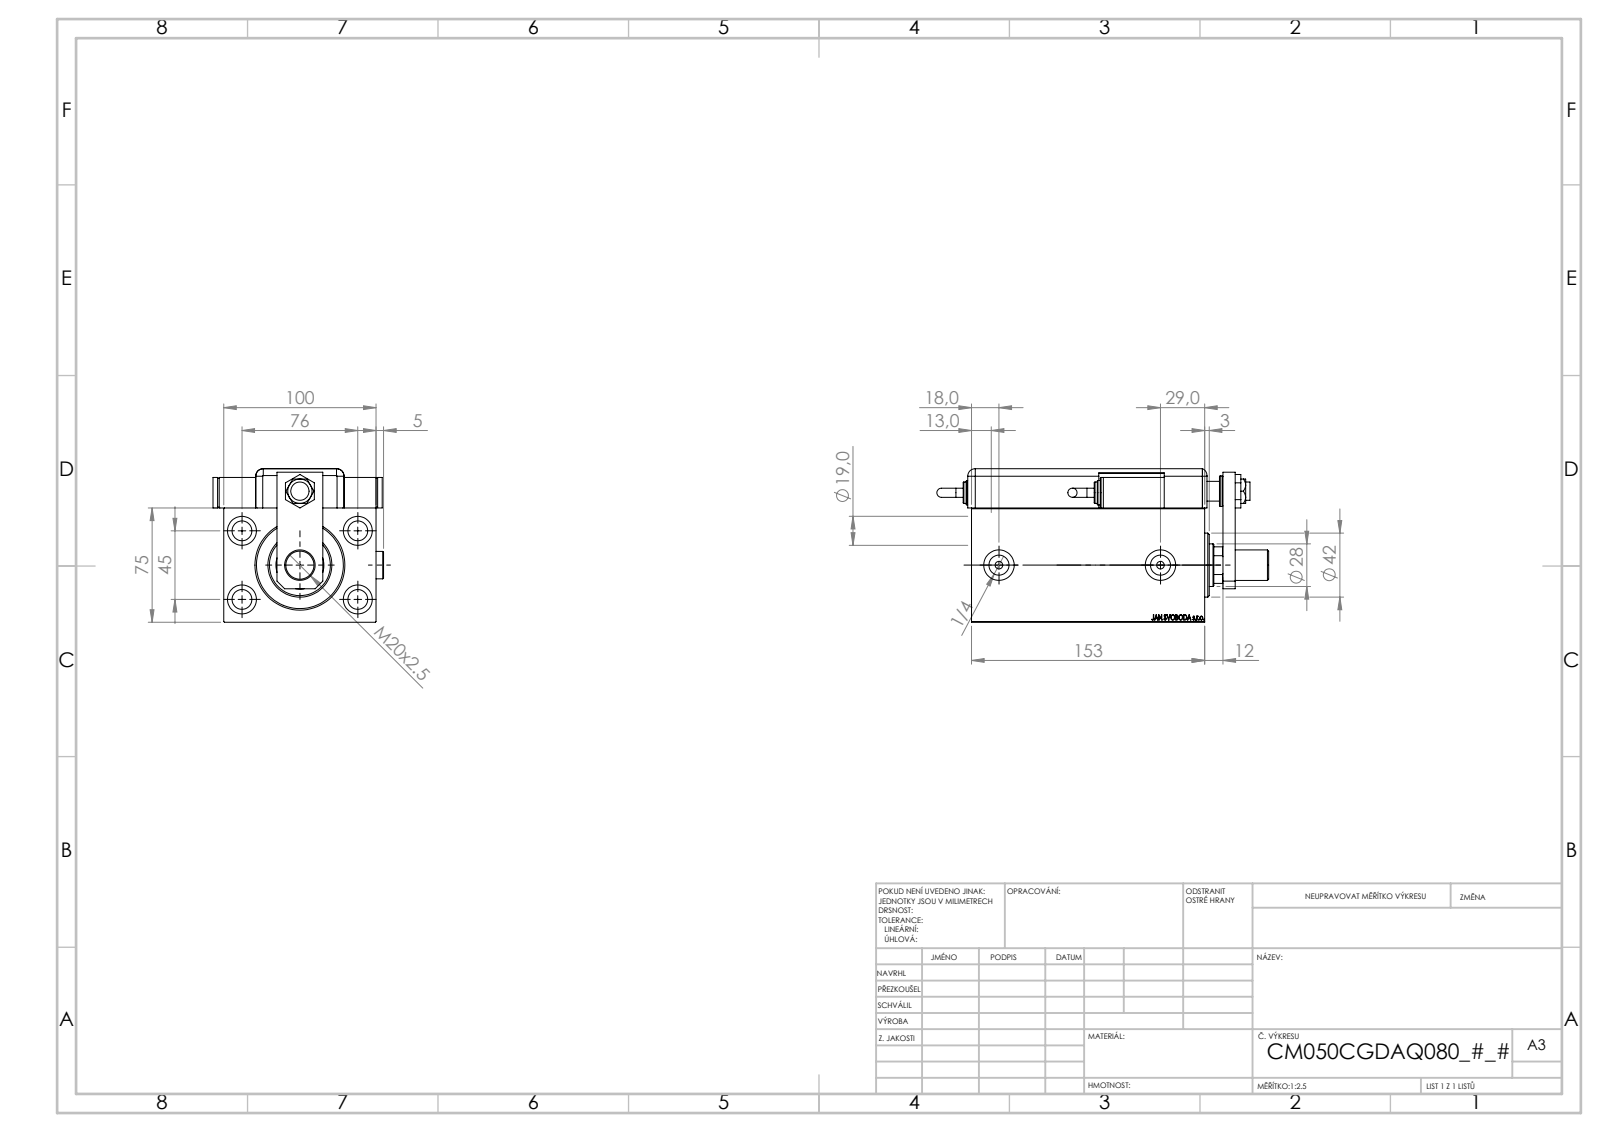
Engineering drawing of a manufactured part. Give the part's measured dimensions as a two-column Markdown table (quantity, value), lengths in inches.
| quantity | value |
| --- | --- |
| part name | V450CM_C_Body; Zatka_OIL_PORT; ZARAZKA_Q; V450CM_MALE_METRIC (+7 more) |
| STEP written by | SolidWorks 2019 (CONFIG_CONTROL_DESIGN) |
| units | inches |
| bodies | 16 solids, 1317 faces (653 planar, 137 cylindrical, 527 other) |
| overall size | 8.573 × 4.406 × 3.969 |
| volume | 68.04 in³ |
| surface area | 342.3 in² |
| round holes (diameter × count) | 0.512 × 5, 0.748 × 4, 0.787 × 3, 0.157 × 2, 0.197 × 2, 0.315 × 2, 0.518 × 2, 0.472 × 1, 0.551 × 1, 0.728 × 1, 1.102 × 1, 1.24 × 1 |
| round bosses / shafts (diameter × count) | 0.787 × 3, 0.709 × 3, 0.63 × 2, 0.551 × 2, 0.236 × 2, 1.654 × 1 |
| partial cylindrical surfaces (radius × count) | 0.197 × 9, 0.394 × 1, 0.531 × 1 |
| main face-to-face distances | 2.953, 0.118, 3.937, 1.016, 3.969, 0.945, 3.85, 0.898, 0.551, 3.11 |
| hole center spacings | 1.739, 1.772, 1.813, 2.992, 3.17, 3.477, 0.787, 1.909 |
